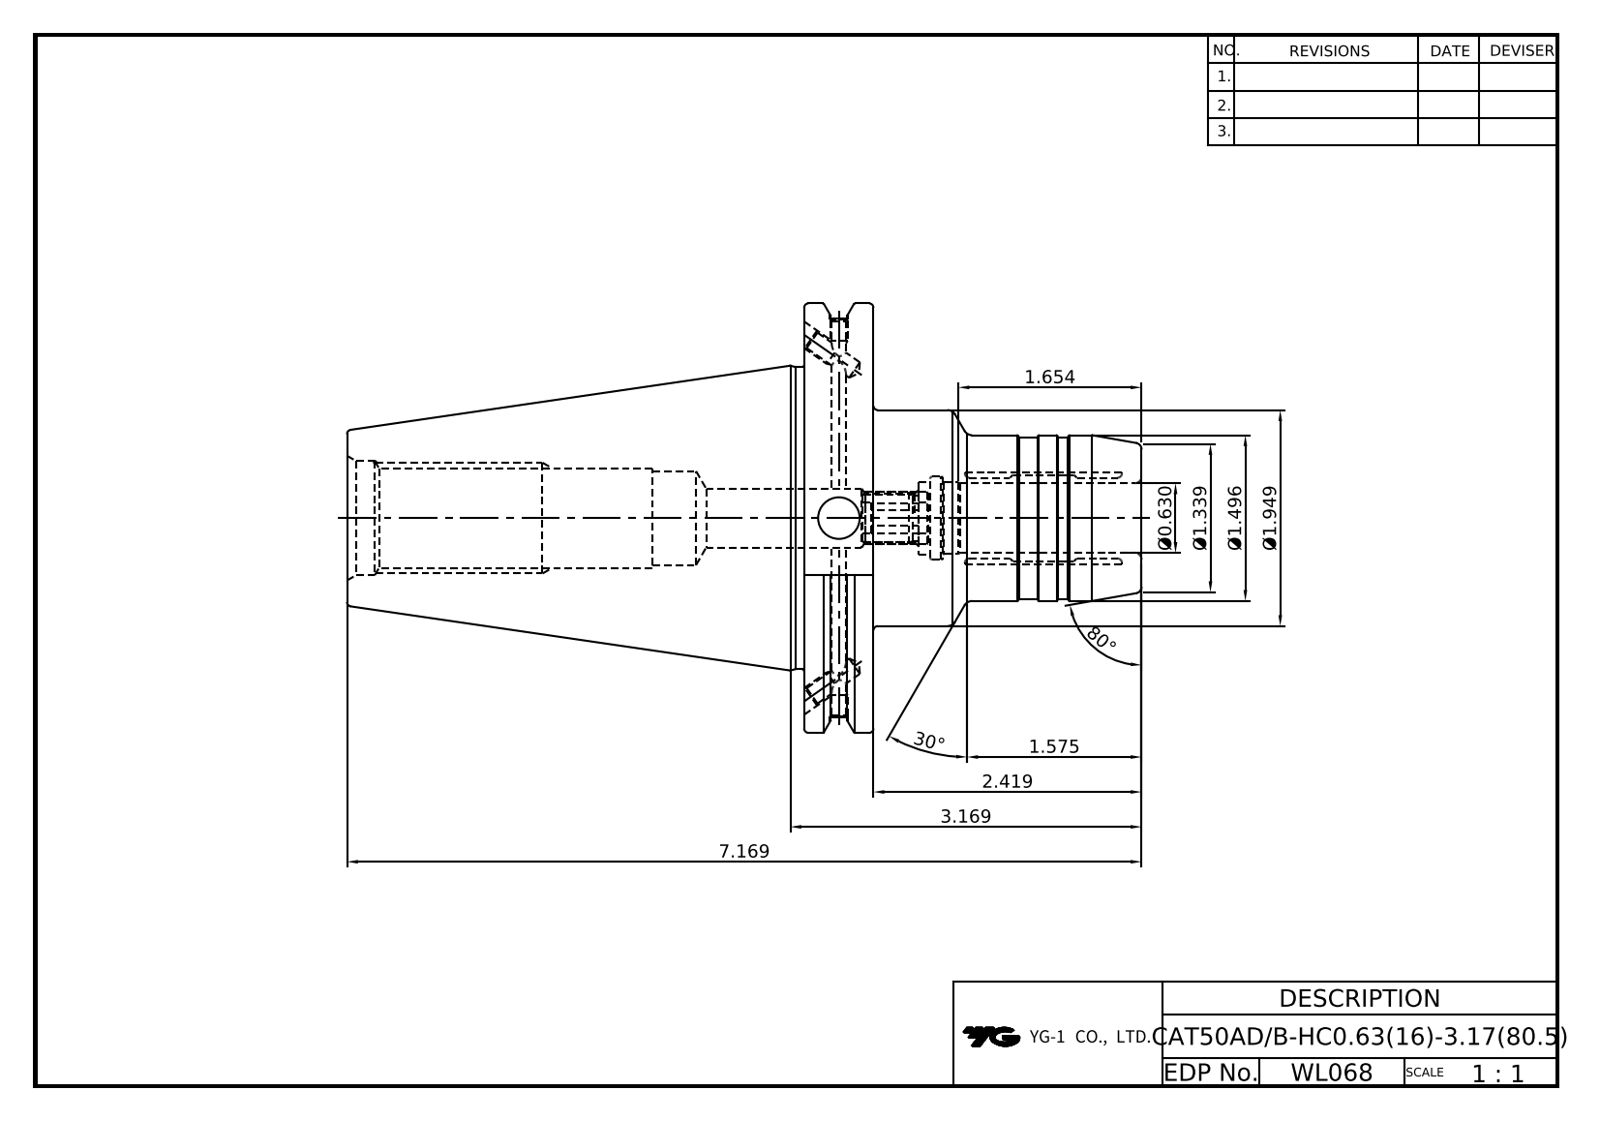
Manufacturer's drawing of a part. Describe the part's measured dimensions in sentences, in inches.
The part is named "LO-CAT50ADB-HC16-80.5". Its 3-D file was written by "Autodesk Inventor 2022 (AUTOMOTIVE_DESIGN)". It is 1 solid with 108 faces: 37 planar, 33 cylindrical and 38 other. Overall it measures 7.169 by 3.875 by 3.728 inches. Its volume is 24.42 cubic inches and its surface area 84.34 square inches. Round holes: 2 of diameter 0.128, 2 of diameter 0.163, 2 of diameter 0.165, 2 of diameter 0.197, 1 of diameter 0.375, 1 of diameter 0.43, 1 of diameter 0.531, 1 of diameter 0.63, 1 of diameter 0.654, 1 of diameter 0.807, 1 of diameter 0.865, 1 of diameter 1.031. Round bosses or shafts: 1 of diameter 3.875, 1 of diameter 3.594, 1 of diameter 2.726, 1 of diameter 1.949, 1 of diameter 1.496, 1 of diameter 1.457. The main face-to-face distances are 0.625, 3.044, 2.419, 4.125, 4.75, 7.169, 2.875, 1.02, 4.363, 0.238.
